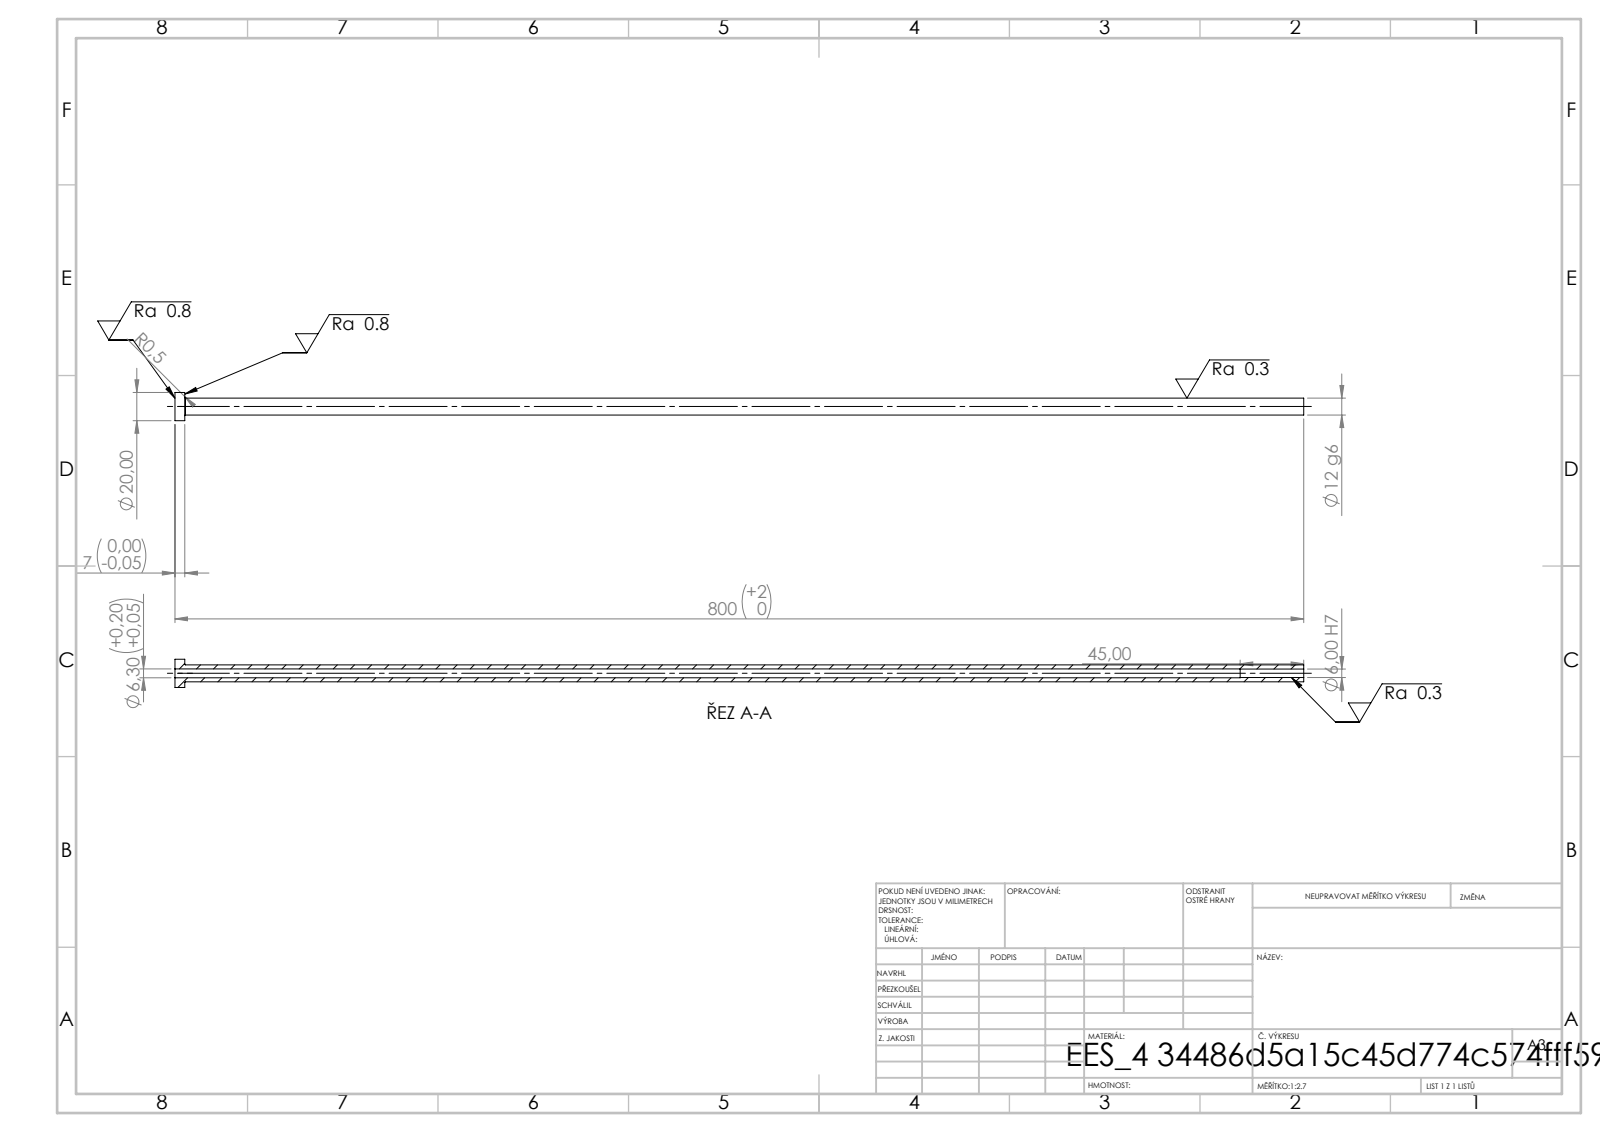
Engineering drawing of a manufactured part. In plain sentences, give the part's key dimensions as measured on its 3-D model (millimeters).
Its 3-D file was written by "SolidWorks 2019 (CONFIG_CONTROL_DESIGN)". It is 1 solid with 14 faces: 4 planar, 8 cylindrical and 2 other. Overall it measures 800 by 20 by 20 millimeters. Its volume is 67 080 cubic millimeters and its surface area 46 690 square millimeters. Round holes: 1 of diameter 6, 1 of diameter 6.3. Round bosses or shafts: 1 of diameter 20, 1 of diameter 12. The main face-to-face distances are 7, 800, 793, 755, 748, 45.
